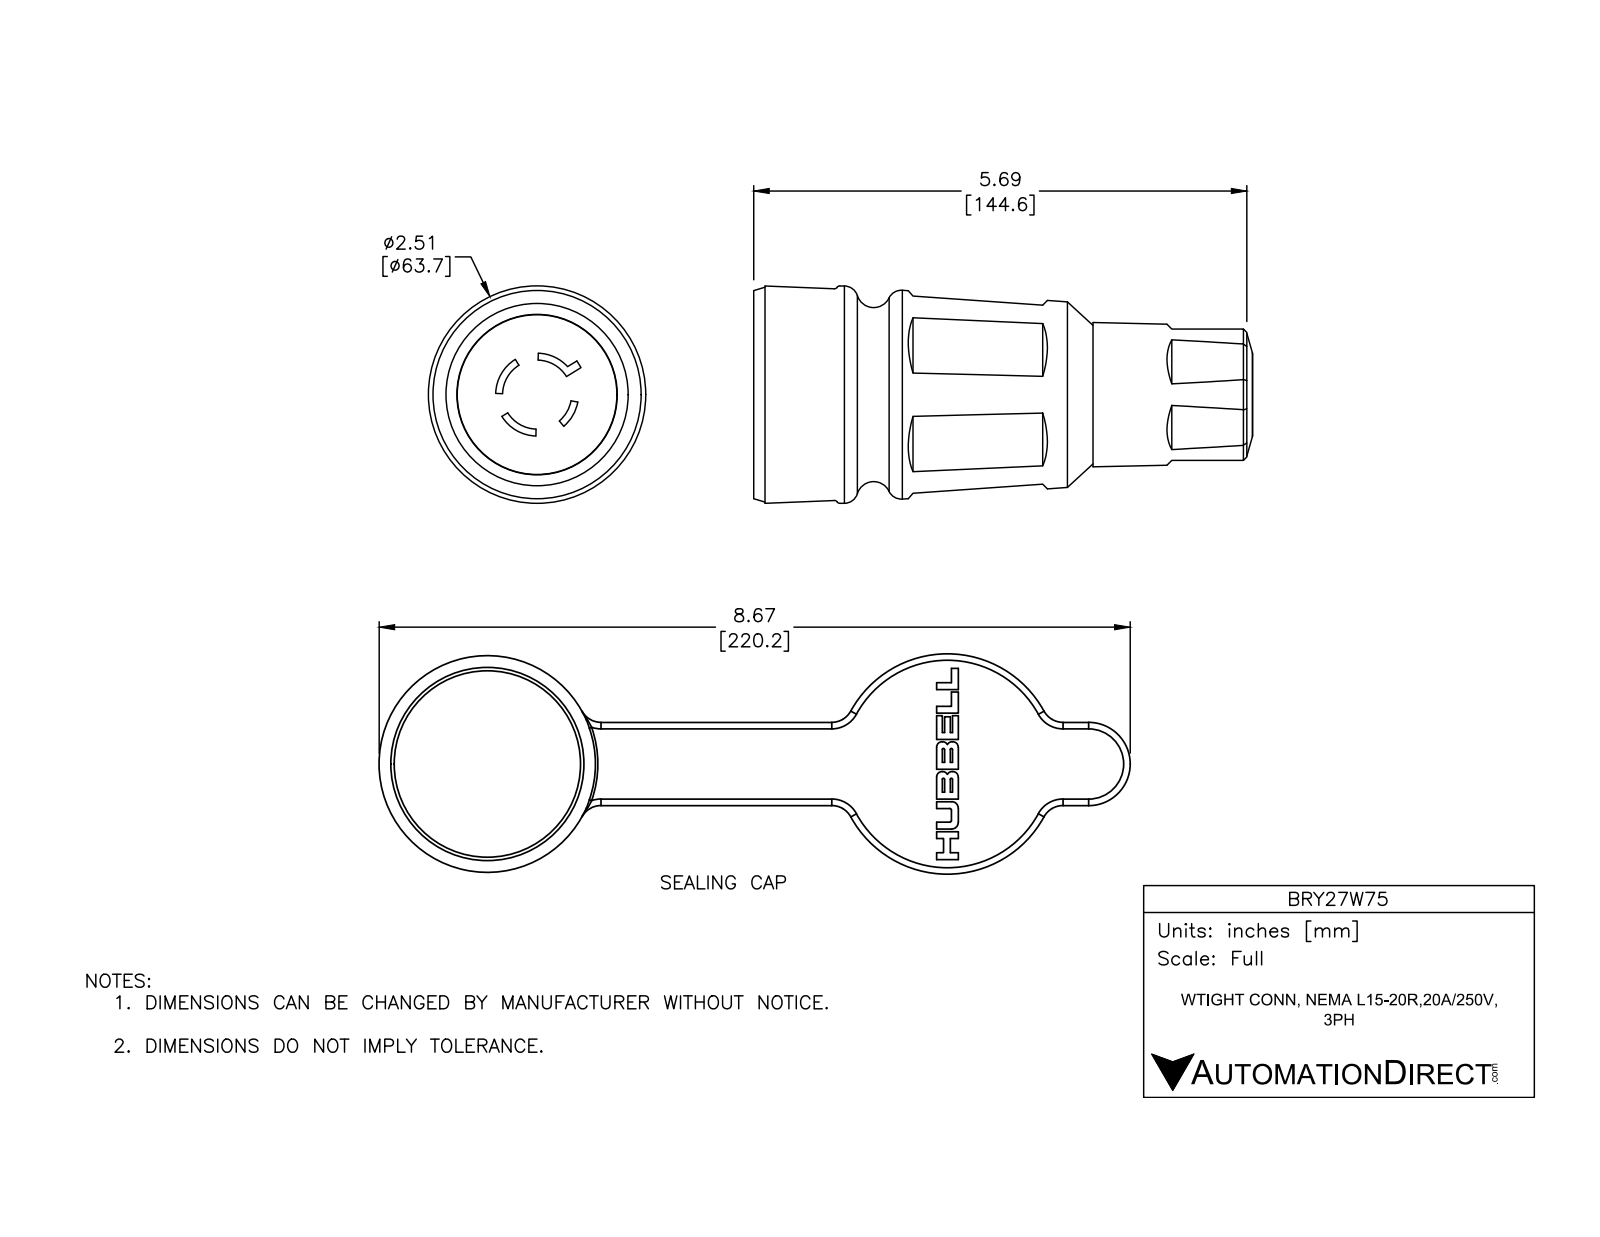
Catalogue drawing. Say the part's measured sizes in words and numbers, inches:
The part is named "BRY27W75; BRY27W-CAP; BRY27W75-CONNECTOR". Its 3-D file was written by "SolidWorks 2016 (AUTOMOTIVE_DESIGN)". It is 5 solids with 186 faces: 71 planar, 53 cylindrical and 62 other. Overall it measures 8.608 by 5.759 by 2.52 inches. Its volume is 18.27 cubic inches and its surface area 125.1 square inches. Round holes: 1 of diameter 0.866, 1 of diameter 1.417, 1 of diameter 1.772, 1 of diameter 1.85, 1 of diameter 2.087, 1 of diameter 2.102. Round bosses or shafts: 1 of diameter 2.52, 1 of diameter 2.508, 1 of diameter 2.425, 1 of diameter 2.205, 1 of diameter 2.037, 1 of diameter 1.843, 1 of diameter 1.24. Partial cylindrical surfaces (rounded edges, fillets, slot ends): 4 of radius 0.069, 4 of radius 0.236, 2 of radius 0.157, 1 of radius 0.399, 1 of radius 0.477, 1 of radius 0.482. The main face-to-face distances are 0.146, 0.502, 0.648, 1.354, 0.852, 0.706, 0.778, 0.276, 0.13, 0.576. The hole center spacings are 5.228.
